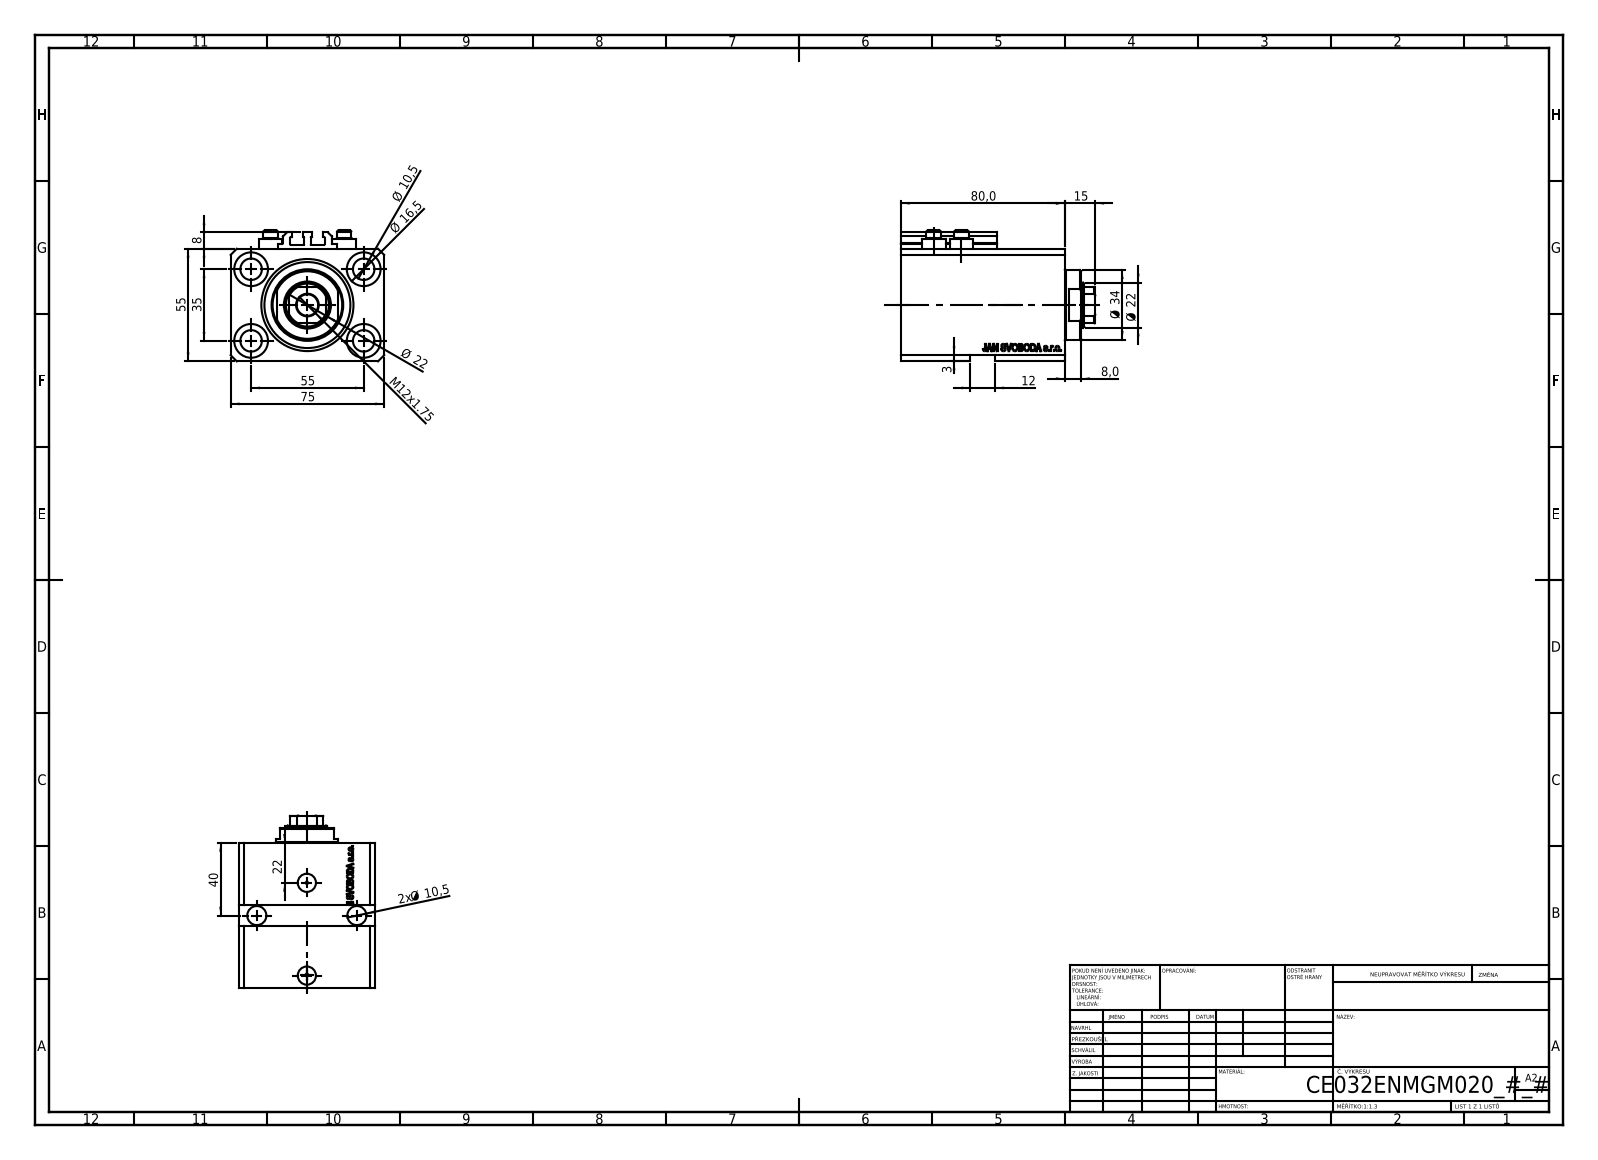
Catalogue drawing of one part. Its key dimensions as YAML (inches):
part_name: "ALLEN BOLT V250CE; V250CE_E_Body; V250CE_C_VCP; V250CE_VC_E"
step_written_by: "SolidWorks 2019 (CONFIG_CONTROL_DESIGN)"
units: inches
bodies: {solids: 8, faces: 1064, planar: 514, cylindrical: 126, other: 424}
overall_size: [3.74, 2.953, 2.52]
volume: 17.32
surface_area: 115.4
round_holes:
  - {diameter: 0.413, count: 7}
  - {diameter: 0.049, count: 4}
  - {diameter: 0.157, count: 4}
  - {diameter: 0.65, count: 4}
  - {diameter: 0.394, count: 2}
  - {diameter: 0.518, count: 2}
  - {diameter: 0.787, count: 2}
  - {diameter: 0.866, count: 1}
  - {diameter: 1.26, count: 1}
  - {diameter: 1.772, count: 1}
round_bosses_or_shafts:
  - {diameter: 0.457, count: 4}
  - {diameter: 0.276, count: 4}
  - {diameter: 1.339, count: 1}
partial_cylinders:
  - {radius: 0.008, count: 10}
  - {radius: 0.413, count: 1}
face_to_face_distances: [2.165, 2.953, 0.591, 3.15, 2.559, 0.118, 2.169, 0.39, 2.76, 2.126]
hole_center_spacings: [1.283, 2.165, 0.535, 0.555, 0.783, 0.792, 1.016, 1.121]
